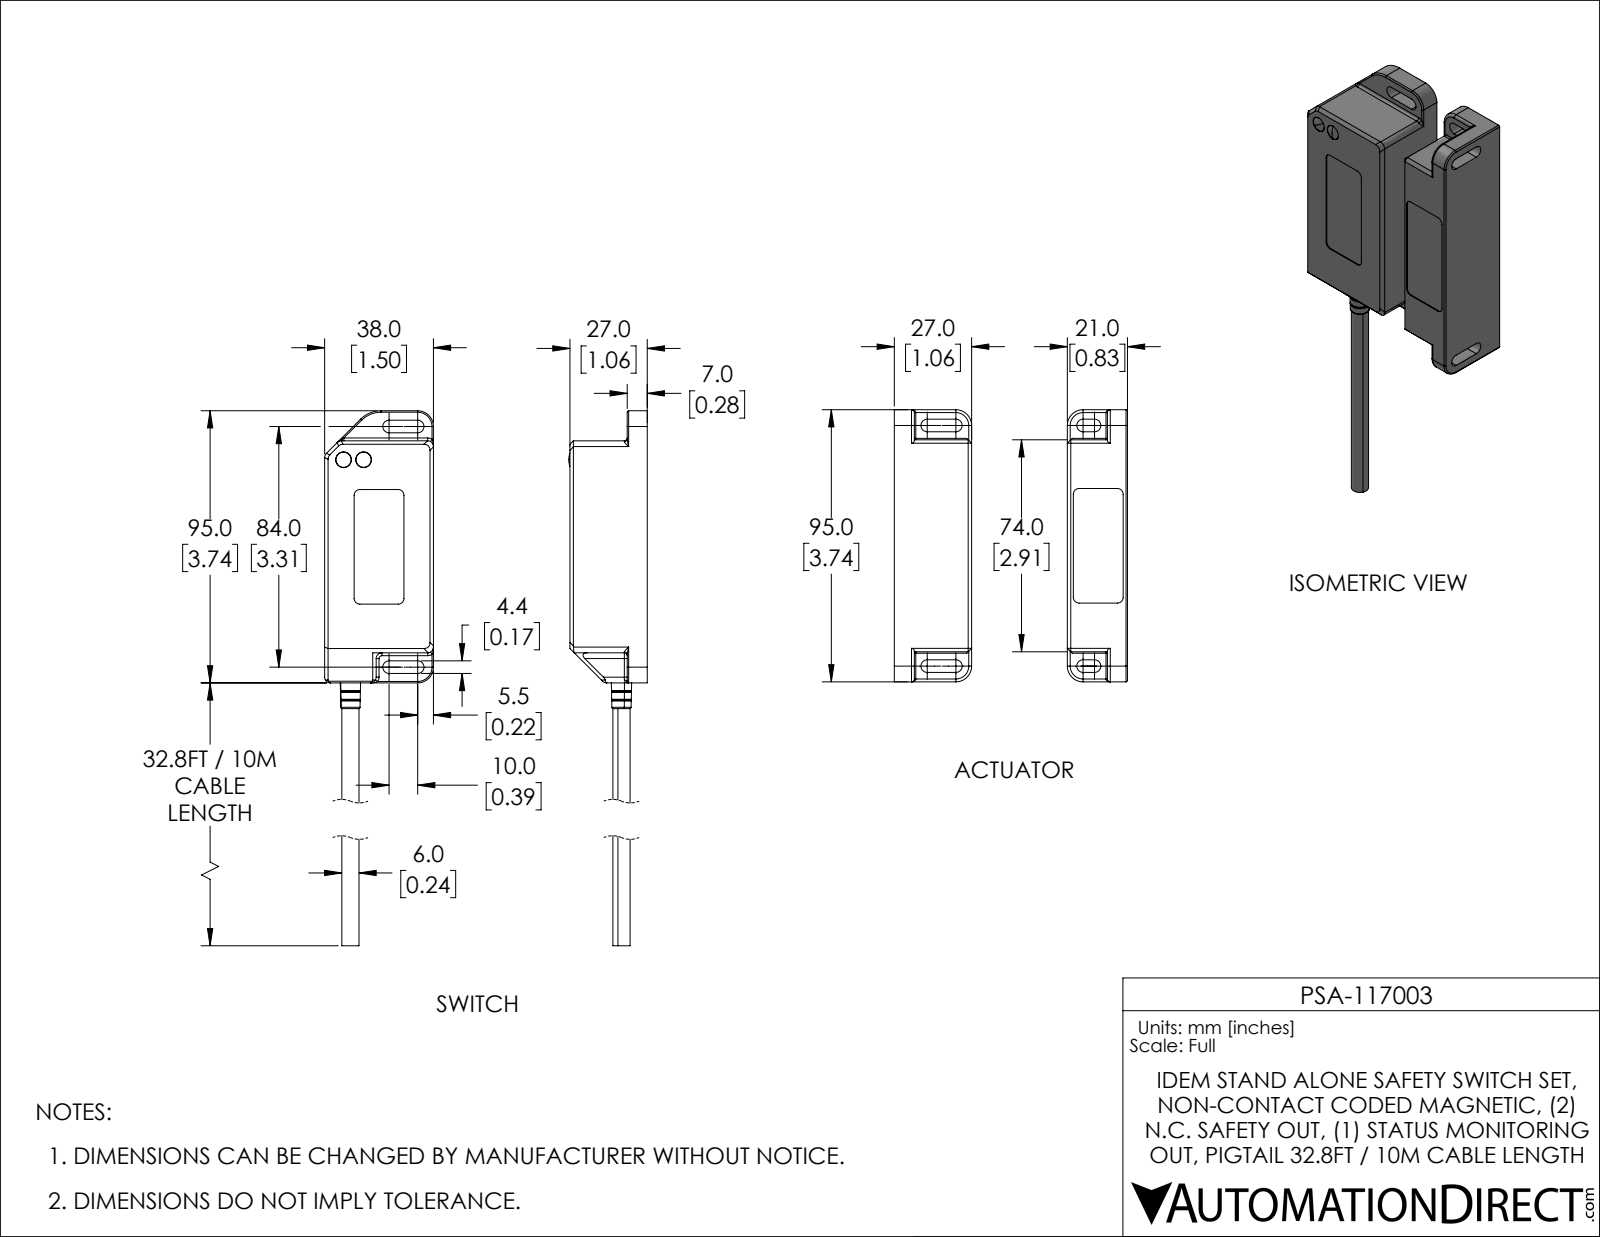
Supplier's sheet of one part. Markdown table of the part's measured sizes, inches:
| quantity | value |
| --- | --- |
| part name | 117-PSA |
| STEP written by | SolidWorks 2019 (AUTOMOTIVE_DESIGN) |
| units | inches |
| bodies | 2 solids, 943 faces (441 planar, 246 cylindrical, 256 other) |
| overall size | 7.092 × 2.717 × 1.079 |
| volume | 2.899 in³ |
| surface area | 67.5 in² |
| round holes (diameter × count) | 0.116 × 2, 0.217 × 2, 0.323 × 1 |
| round bosses / shafts (diameter × count) | 0.209 × 2, 0.197 × 2, 0.177 × 2, 0.079 × 2, 0.339 × 1, 0.299 × 1, 0.28 × 1, 0.236 × 1 |
| partial cylindrical surfaces (radius × count) | 0.02 × 88, 0.079 × 18, 0.087 × 12, 0.039 × 11, 0.012 × 8, 0.217 × 6, 0.008 × 4, 0.118 × 4 |
| main face-to-face distances | 0.079, 1.89, 1.22, 0.976, 0.913, 0.063, 0.472, 0.748, 1.055, 0.992 |
| hole center spacings | 0.276 |
